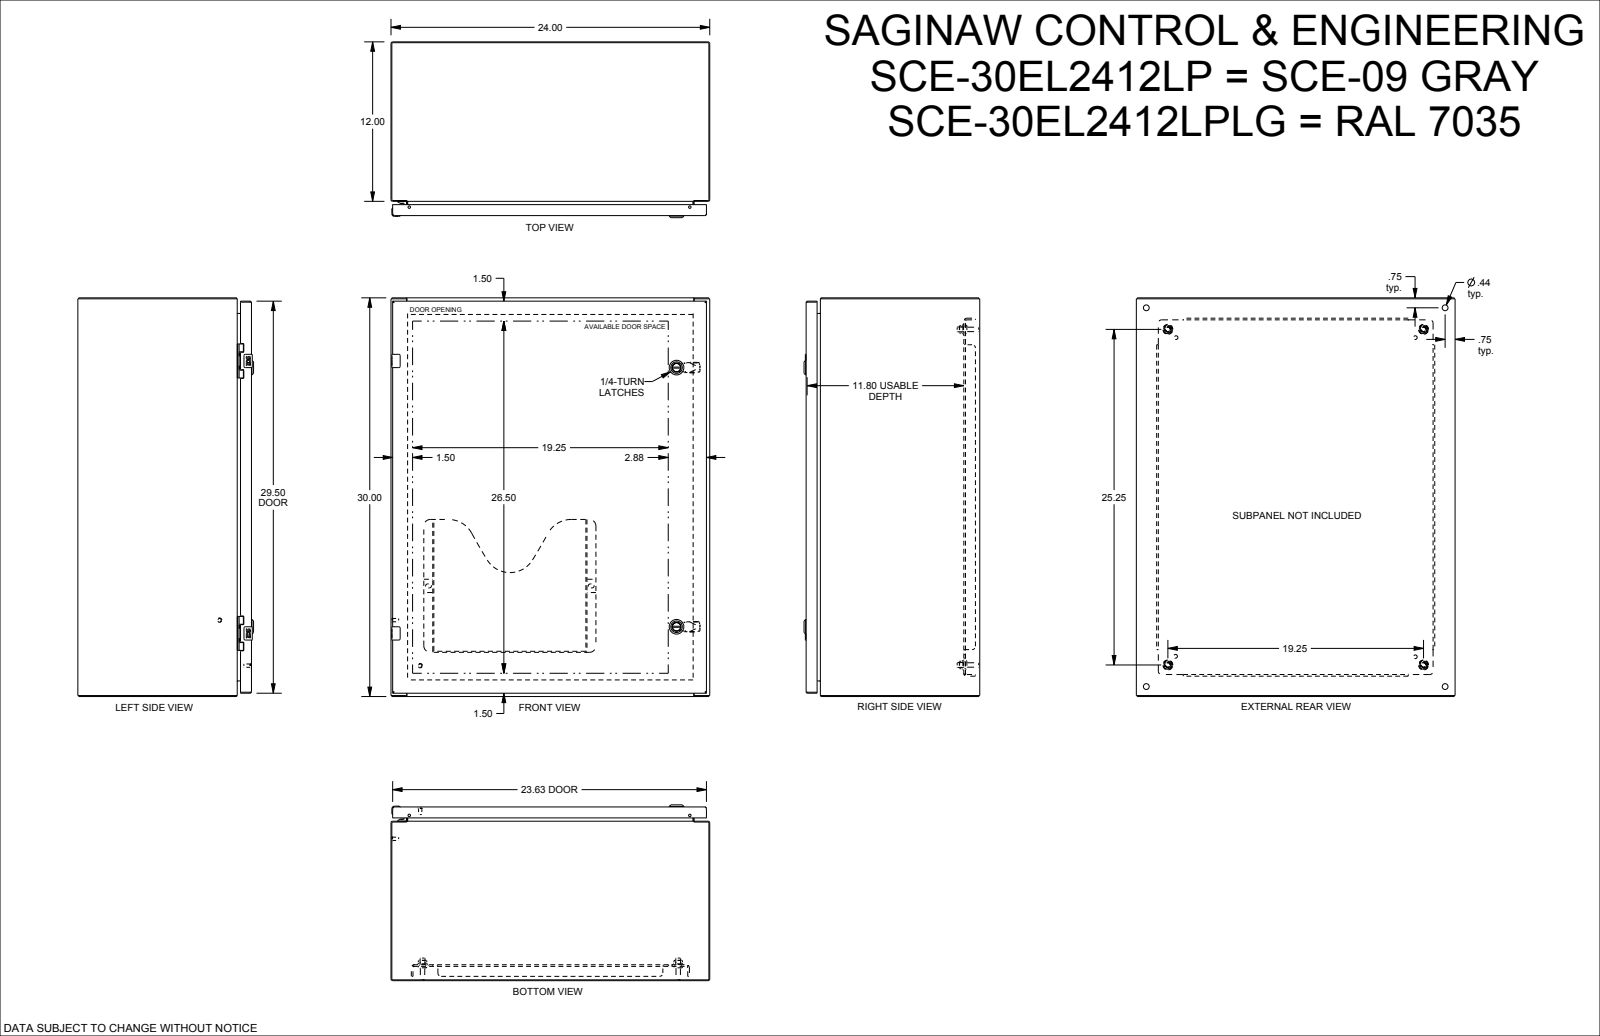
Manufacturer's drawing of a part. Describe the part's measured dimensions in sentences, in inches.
The part is named "SCE-30EL2412LP". Its 3-D file was written by "SolidWorks 2021 (AUTOMOTIVE_DESIGN)". It is 47 solids with 2843 faces: 1115 planar, 858 cylindrical and 870 other. Overall it measures 30 by 24 by 13.23 inches. Its volume is 319.4 cubic inches and its surface area 7 751 square inches. Round holes: 4 of diameter 0.172, 4 of diameter 0.205, 4 of diameter 0.244, 4 of diameter 0.266, 4 of diameter 0.281, 4 of diameter 0.367, 4 of diameter 0.375, 4 of diameter 0.437, 4 of diameter 0.5, 2 of diameter 0.04, 2 of diameter 0.188, 2 of diameter 0.197. Round bosses or shafts: 6 of diameter 0.17, 4 of diameter 0.366, 4 of diameter 0.332, 4 of diameter 0.25, 4 of diameter 0.248, 4 of diameter 0.24, 3 of diameter 0.196, 2 of diameter 1.102. Partial cylindrical surfaces (rounded edges, fillets, slot ends): 56 of radius 0.012, 28 of radius 0.01, 24 of radius 0.015, 20 of radius 0.02, 17 of radius 0.04, 13 of radius 0.06, 12 of radius 0.029, 12 of radius 0.1. The main face-to-face distances are 0.075, 0.06, 23.925, 13.073, 12.998, 13.013, 12.938, 1.2, 11.873, 1. The hole center spacings are 0.985, 20.5, 0.875, 26.924, 0.02, 0.493, 0.494, 2.298.
